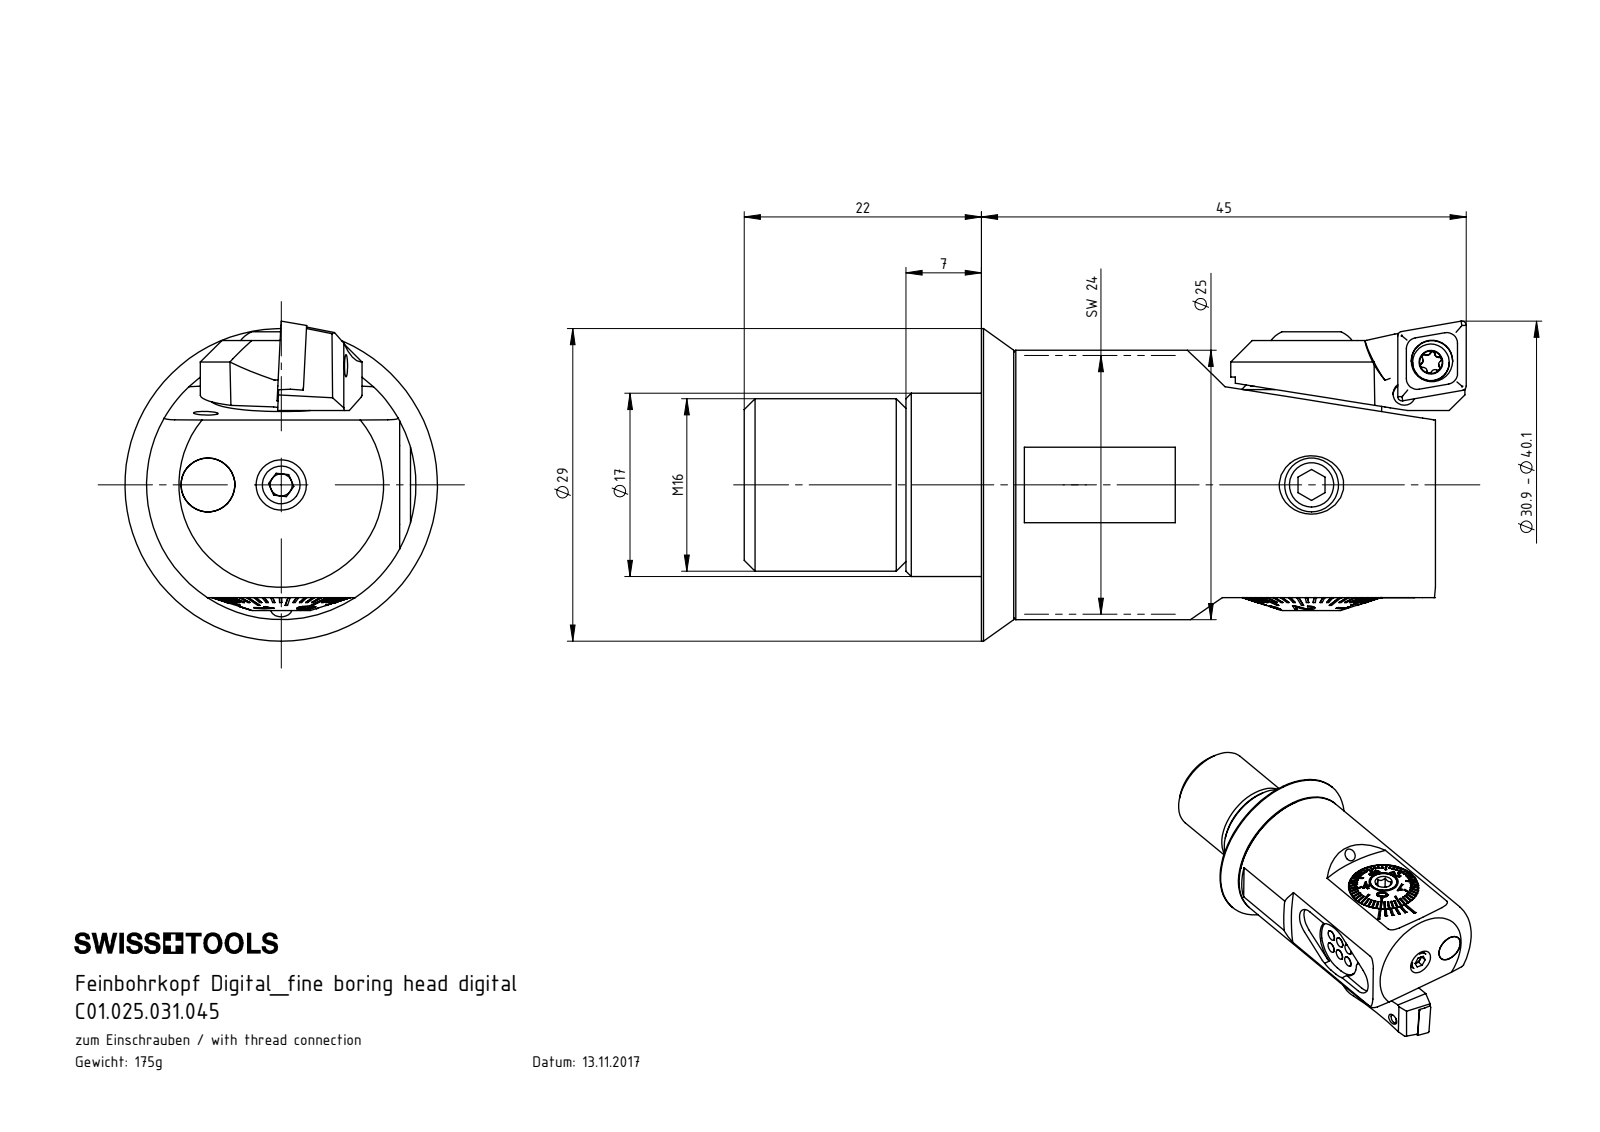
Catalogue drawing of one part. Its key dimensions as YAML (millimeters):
part_name: "F25-ER1.101.008_A; PEE-DA1.011.026_A; T7 M2.5 x 6_PreviewCfg; HP5-F25.DA1.045_A (+8 more)"
step_written_by: "SolidWorks 2017 (CONFIG_CONTROL_DESIGN)"
units: millimeters
bodies: {solids: 22, faces: 927, planar: 415, cylindrical: 197, other: 315}
overall_size: [67, 29.7, 29]
volume: 22478
surface_area: 15054
round_holes:
  - {diameter: 2, count: 4}
  - {diameter: 2.05, count: 3}
  - {diameter: 4.2, count: 2}
  - {diameter: 0.7, count: 1}
  - {diameter: 2.1, count: 1}
  - {diameter: 2.4, count: 1}
  - {diameter: 2.7, count: 1}
  - {diameter: 2.8, count: 1}
  - {diameter: 3, count: 1}
  - {diameter: 3.3, count: 1}
  - {diameter: 3.85, count: 1}
  - {diameter: 5, count: 1}
round_bosses_or_shafts:
  - {diameter: 1.9, count: 6}
  - {diameter: 5, count: 2}
  - {diameter: 4.95, count: 2}
  - {diameter: 2.5, count: 2}
  - {diameter: 29, count: 1}
  - {diameter: 25, count: 1}
  - {diameter: 16, count: 1}
  - {diameter: 12.98, count: 1}
partial_cylinders:
  - {radius: 0.21, count: 6}
  - {radius: 0.36, count: 5}
  - {radius: 0.5, count: 4}
  - {radius: 1.1, count: 3}
  - {radius: 1.2, count: 3}
  - {radius: 1.32, count: 2}
  - {radius: 1.4, count: 2}
  - {radius: 3.1, count: 2}
face_to_face_distances: [3, 42.15, 39.15, 8, 1.5, 4.25, 15, 19.95, 0.8, 3.1]
hole_center_spacings: [2.6, 0.68, 3.84, 3.99, 4.48, 6.8, 9.46, 16.5]
